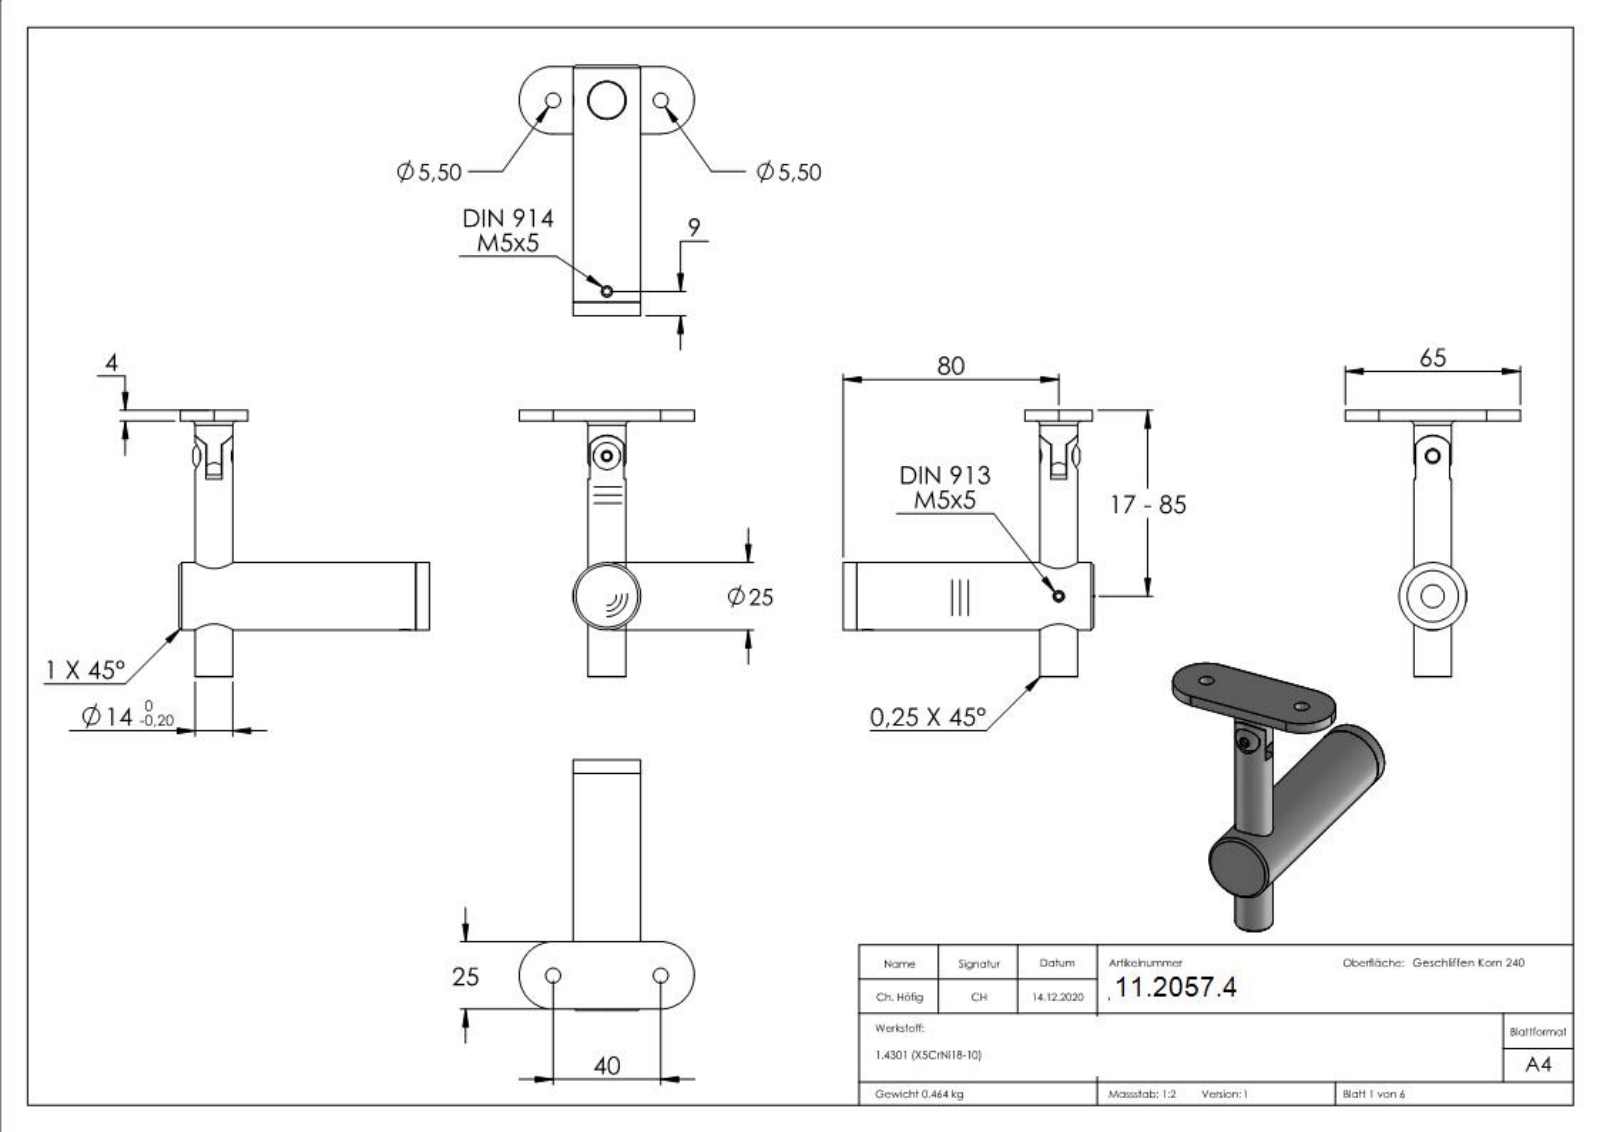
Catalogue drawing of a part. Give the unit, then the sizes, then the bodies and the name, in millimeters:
Units: millimetres
Overall size (bounding box): 99 × 93 × 88
Round holes (diameter × count): ⌀4.2 ×3, ⌀5.5 ×3, ⌀8.5 ×1, ⌀10 ×1, ⌀14.2 ×1, ⌀16 ×1, ⌀19 ×1
Round bosses / shafts (diameter × count): ⌀5 ×3, ⌀25 ×1, ⌀14 ×1
Partial cylindrical surfaces — rounded edges, fillets, slot ends (radius × count): R7.75 ×3, R12.5 ×2, R8.1 ×1
Main face-to-face distances: 4, 88, 9.5, 15.5, 9.75, 5.75, 2, 15.25, 83, 25.5
Hole centre spacings: 20, 73.76, 40, 52, 71
Volume: 58 712 mm³ · Surface area: 21 713 mm²
Bodies: 7 solids, 359 faces (148 planar, 76 cylindrical, 135 other)
Part name (STEP PRODUCT): DIN914_DIN 914 M5x5; 5037X-240 Teil1_50377-240 Teil1; DIN914; 5037X-240 Teil4_50374-240 Teil4 (+8 more)
STEP written by: SolidWorks 2018 (CONFIG_CONTROL_DESIGN)
